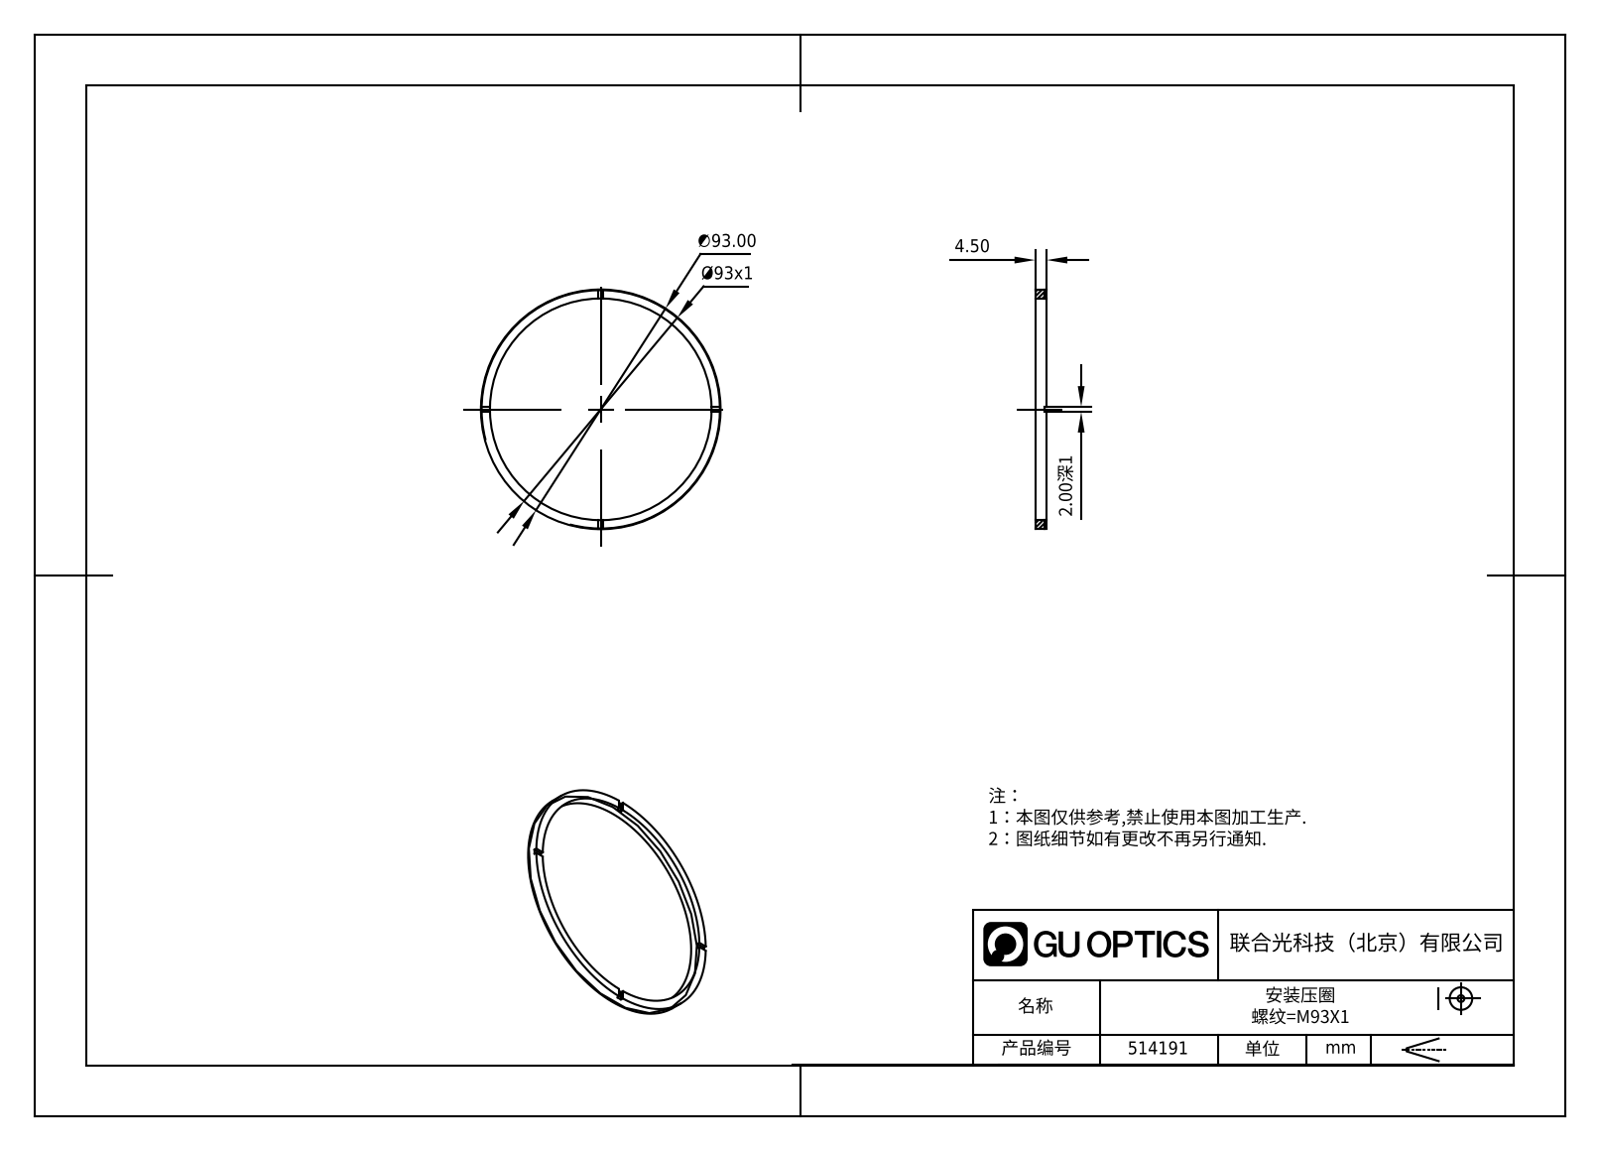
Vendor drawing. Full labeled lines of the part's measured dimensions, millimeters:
Part name (STEP PRODUCT): 514191
STEP written by: SolidWorks 2020 (CONFIG_CONTROL_DESIGN)
Units: millimetres
Bodies: 1 solid, 21 faces (17 planar, 4 cylindrical, 0 other)
Overall size (bounding box): 93 × 93 × 4.5
Volume: 4 400 mm³ · Surface area: 4 511 mm²
Round holes (diameter × count): ⌀86 ×1
Round bosses / shafts (diameter × count): ⌀93 ×1
Main face-to-face distances: 4.5, 3.5, 1, 2
